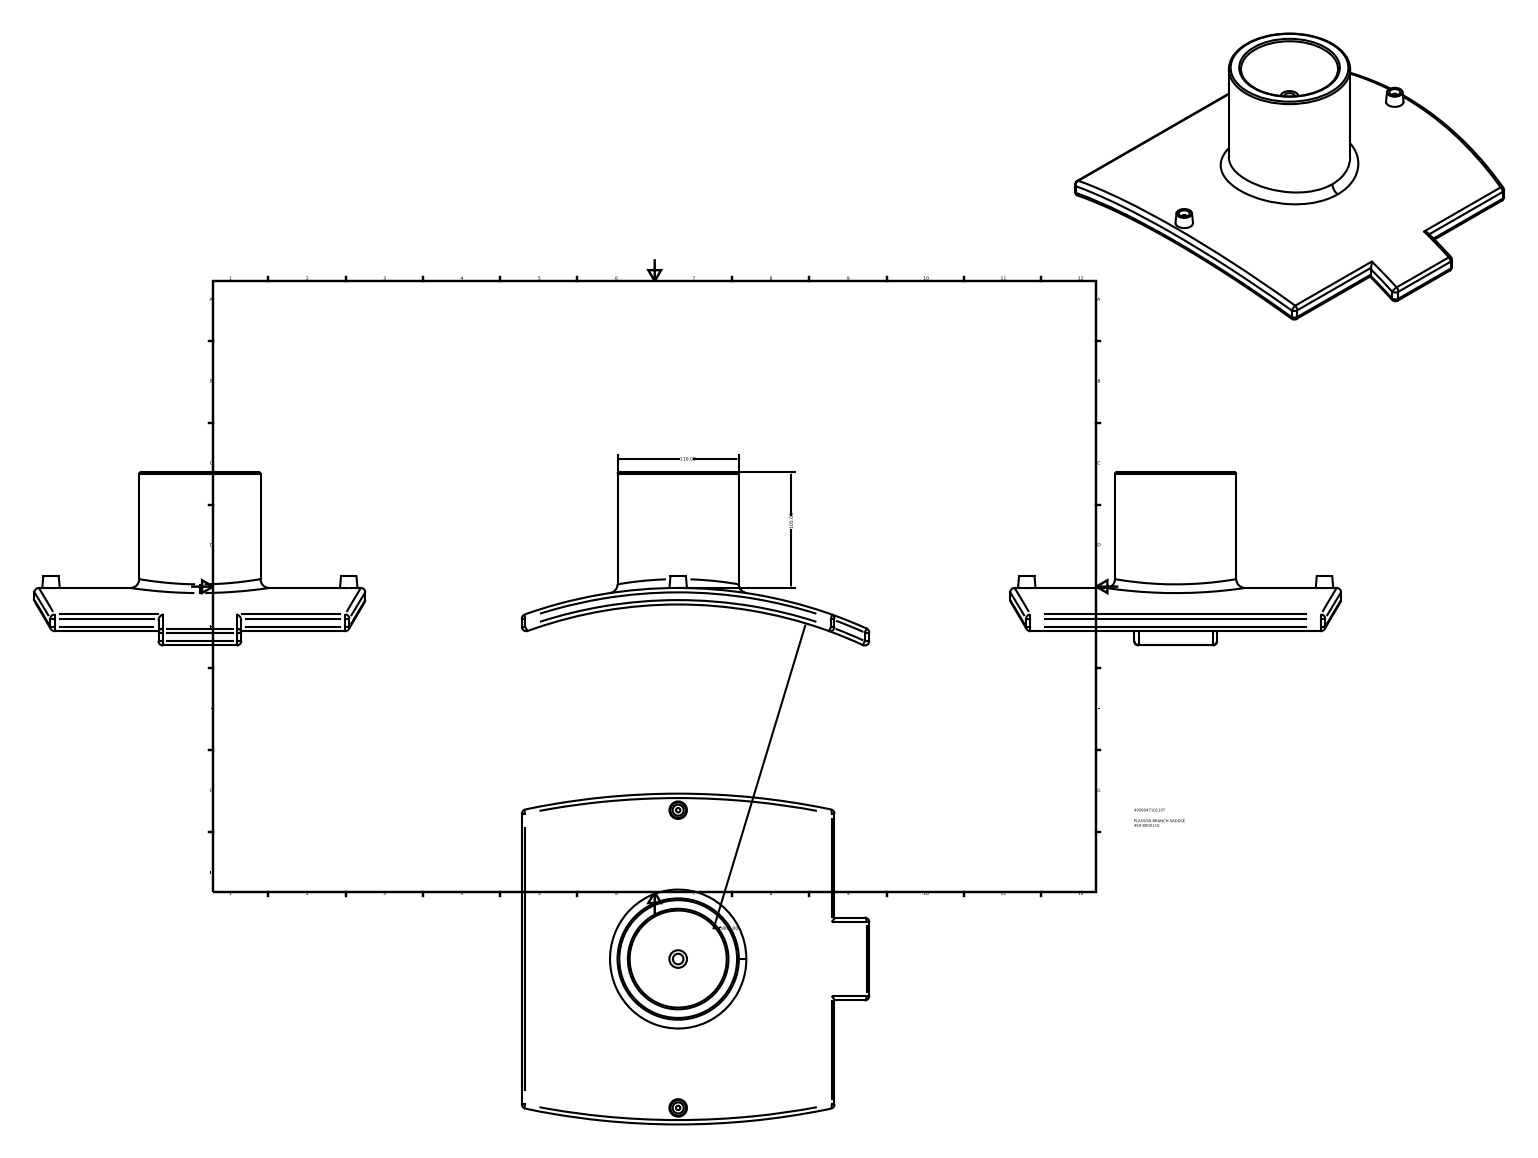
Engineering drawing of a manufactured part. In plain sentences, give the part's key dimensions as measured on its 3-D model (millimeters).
The part is named "495804710110T". Its 3-D file was written by "Autodesk Inventor 2015 (AUTOMOTIVE_DESIGN)". It is 1 solid with 66 faces: 14 planar, 27 cylindrical and 25 other. Overall it measures 315 by 300 by 157.16 millimeters. Its volume is 1 666 000 cubic millimeters and its surface area 259 713 square millimeters. Round holes: 2 of diameter 10, 1 of diameter 9.6, 1 of diameter 88. Round bosses or shafts: 2 of diameter 4, 1 of diameter 110, 1 of diameter 16. Partial cylindrical surfaces (rounded edges, fillets, slot ends): 12 of radius 4, 2 of radius 677.27, 1 of radius 400, 1 of radius 415. The main face-to-face distances are 283.5, 31.5, 315, 75, 94.4, 14, 108.4, 76.9, 62.9, 11. The hole center spacings are 135, 270.
